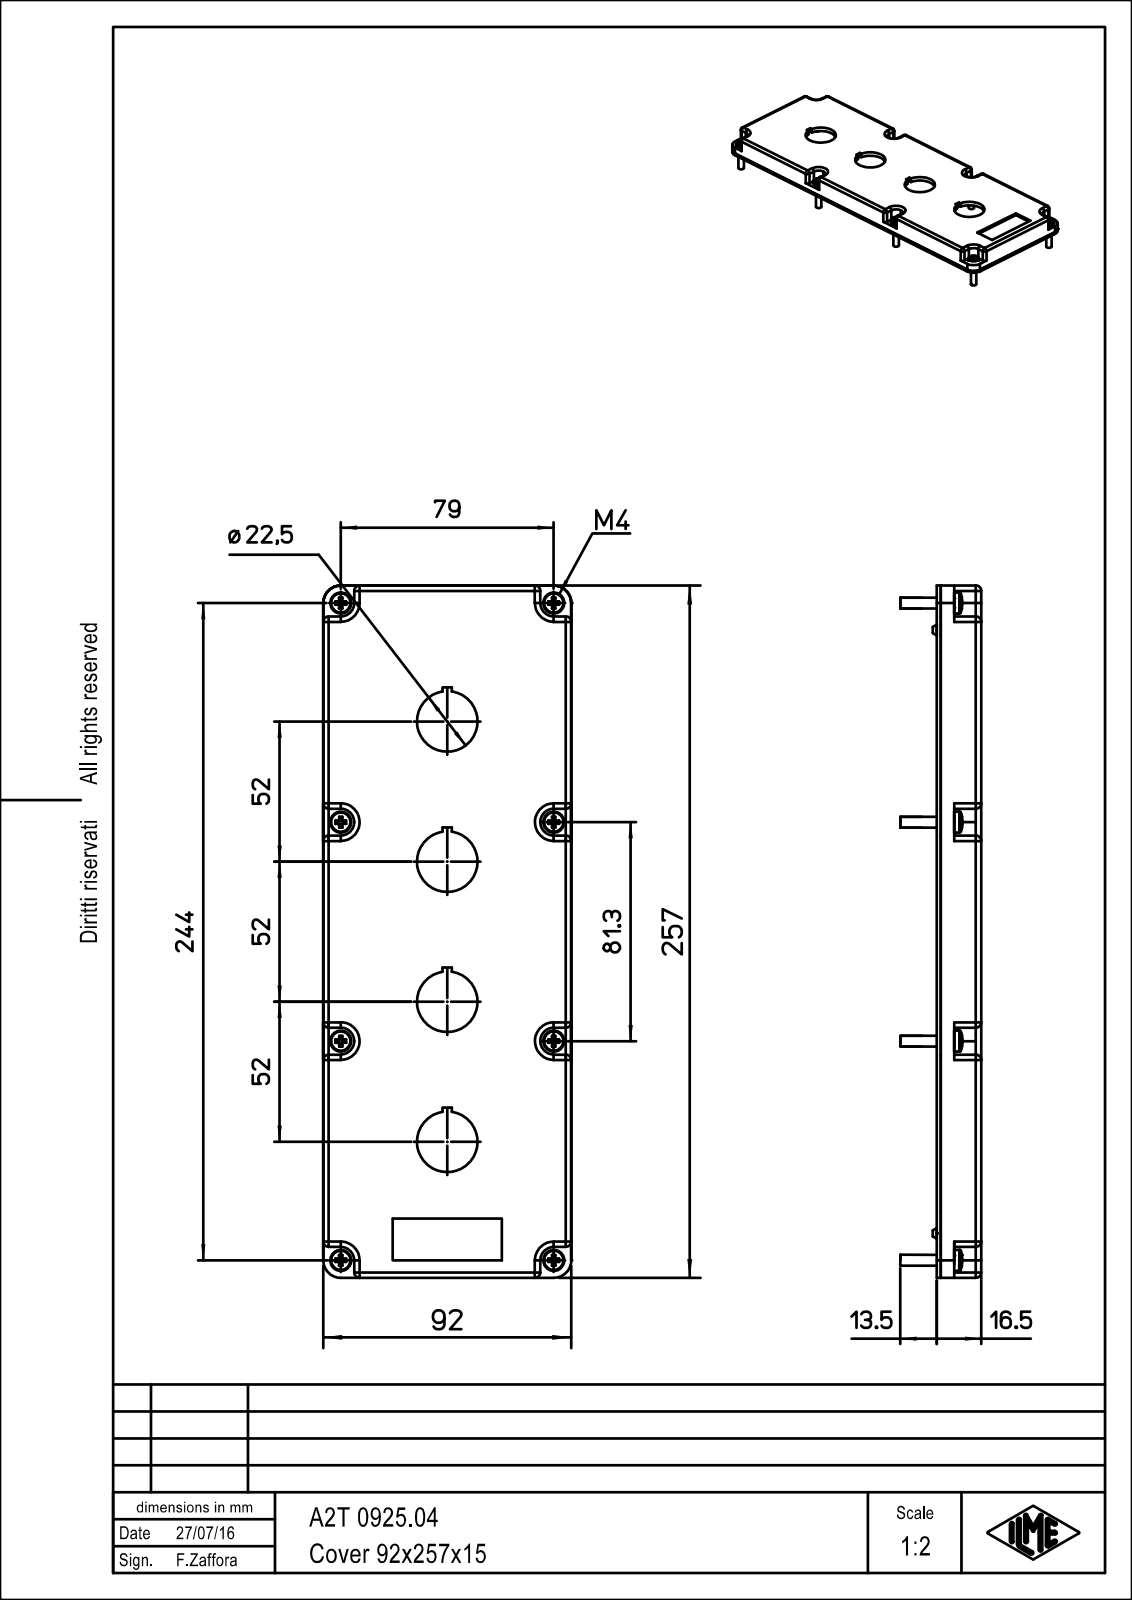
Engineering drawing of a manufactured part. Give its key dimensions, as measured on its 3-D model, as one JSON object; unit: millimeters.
{"part_name": "A2T_0925.04", "step_written_by": "PTC Creo Elements/Direct Modeling 19.0B 21-Mar-2015 (C) Parametric Technology GmbH (AUTOMOTIVE_DESIGN)", "units": "millimeters", "bodies": {"solids": 1, "faces": 782, "planar": 538, "cylindrical": 180, "other": 64}, "overall_size": [257, 92.02, 30.01], "volume_mm3": 110104, "surface_area_mm2": 79695, "round_holes": [[4.5, 8], [22.5, 4], [3.3, 1], [5.8, 1]], "round_bosses_or_shafts": [[7.8, 8], [4, 8], [6, 2], [7, 1], [6.2, 1]], "partial_cylinders_radius": [[2, 29], [0.33, 11], [5, 10], [8, 10], [6.5, 8], [0.5, 4], [0.27, 2], [0.27, 2]], "face_to_face_distances": [3, 13.5, 16.5, 1.5, 12, 15, 89, 92, 86, 254], "hole_center_spacings": [42.13, 54.36, 59.13, 77.48, 79, 81.35, 103.81, 113.4]}
